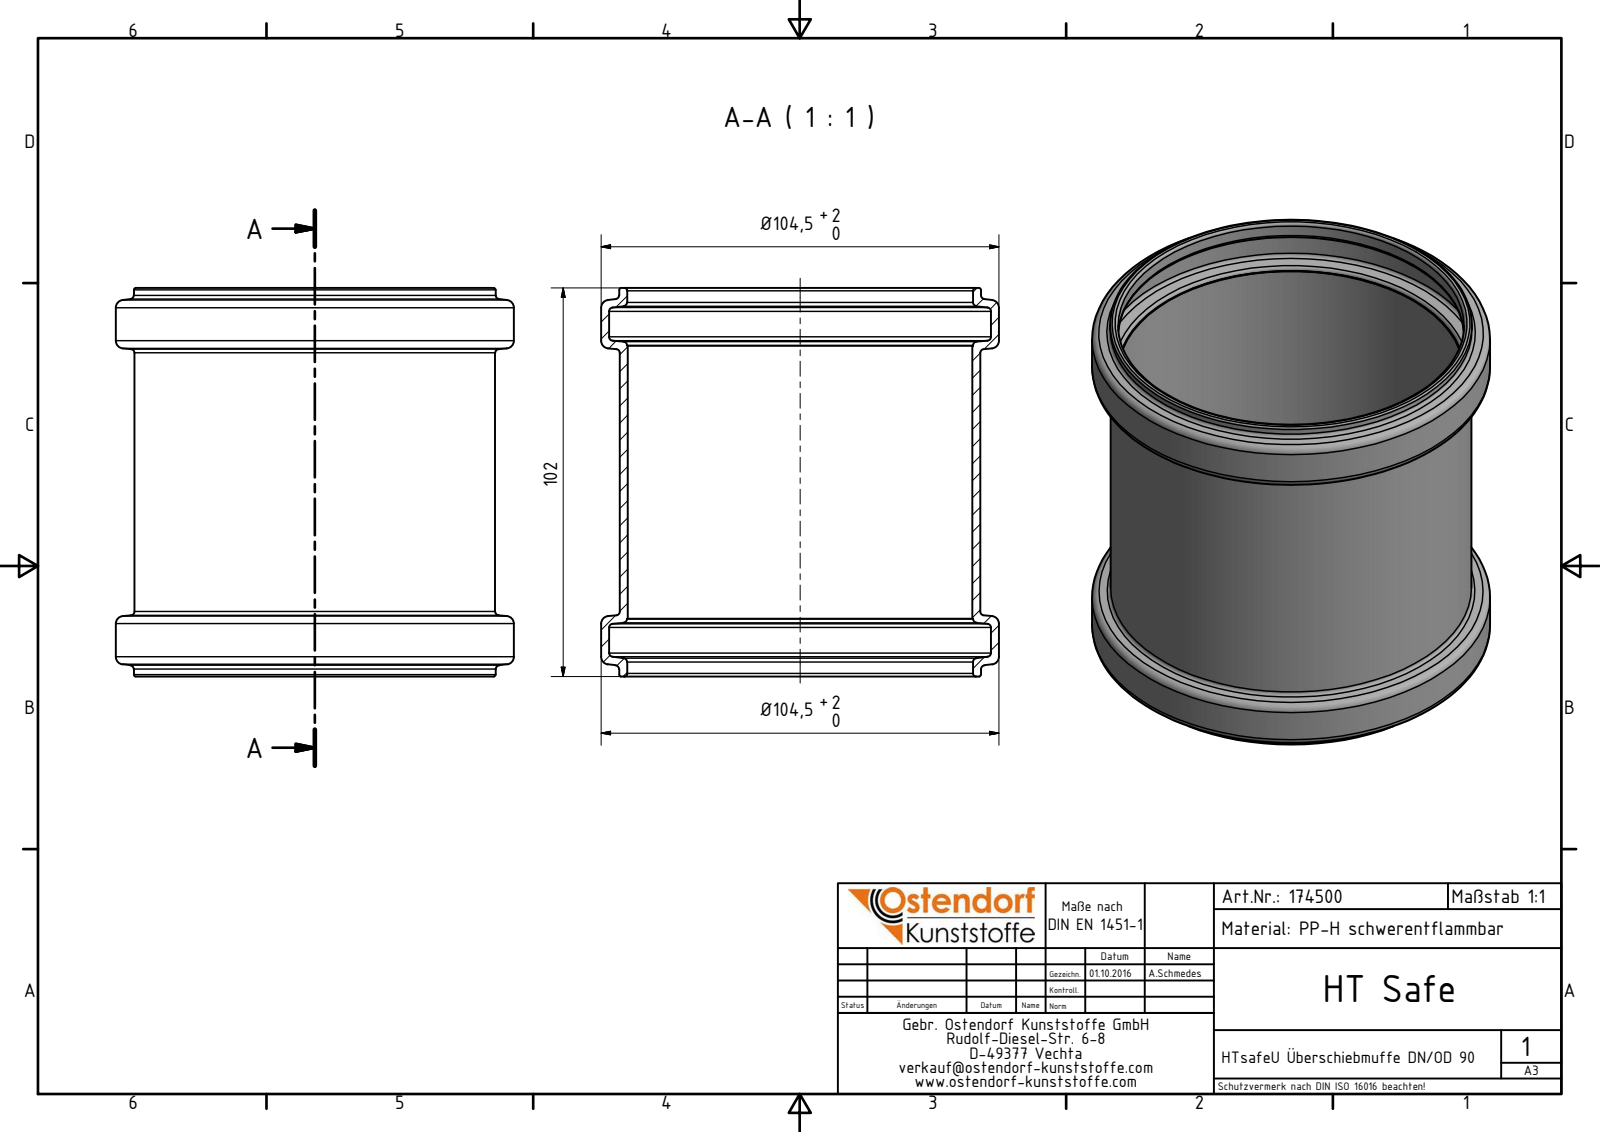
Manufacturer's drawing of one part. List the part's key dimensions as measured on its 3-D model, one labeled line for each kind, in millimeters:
Part name (STEP PRODUCT): 174500 HTsafeU DN_OD 90
STEP written by: Autodesk Inventor 2016 (AUTOMOTIVE_DESIGN)
Units: millimetres
Bodies: 1 solid, 44 faces (4 planar, 12 cylindrical, 28 other)
Overall size (bounding box): 104.5 × 104.5 × 102
Volume: 74 080 mm³ · Surface area: 70 184 mm²
Round holes (diameter × count): ⌀90.5 ×1, ⌀90.8 ×1, ⌀100.3 ×1
Round bosses / shafts (diameter × count): ⌀104.5 ×1, ⌀95 ×1, ⌀94.7 ×1
Main face-to-face distances: 102, 15.21, 86.79, 71.58
